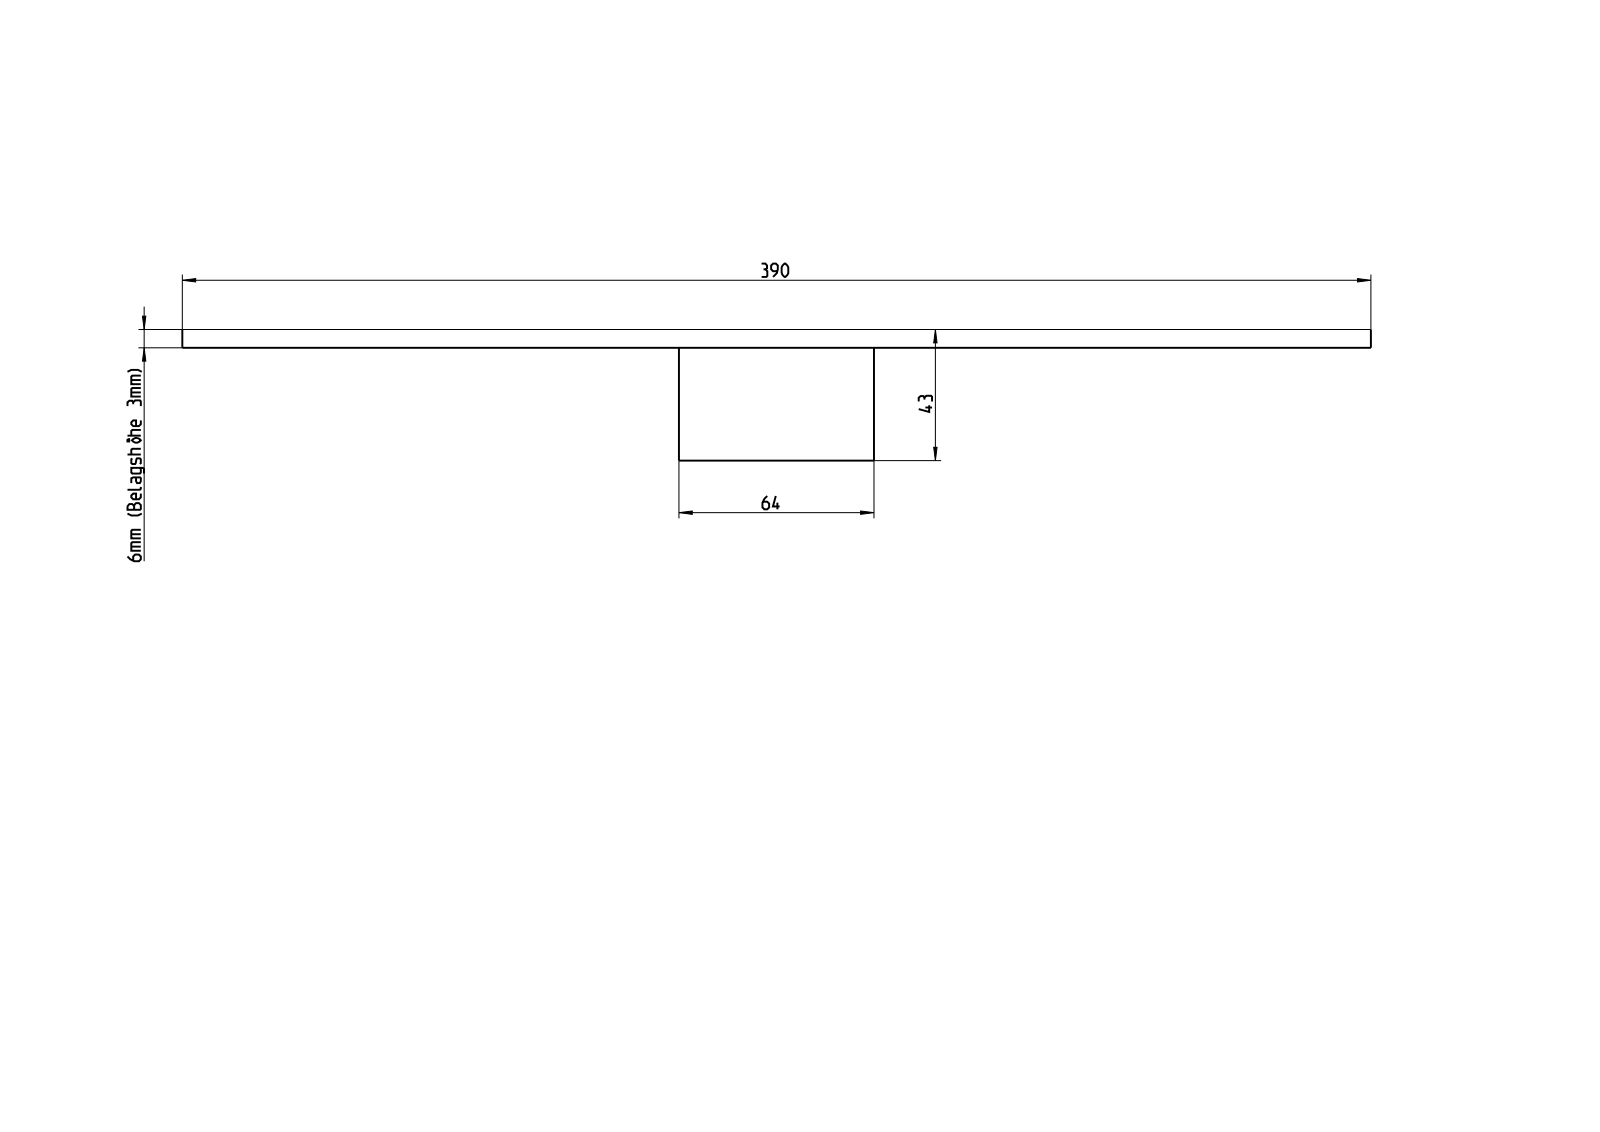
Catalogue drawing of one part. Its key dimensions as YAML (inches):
part_name: "1BKG4002W3LA; AUSLASS; BKG4002W3LA_ASM"
step_written_by: "CREO PARAMETRIC BY PTC INC, 2022024 (AUTOMOTIVE_DESIGN)"
units: inches
bodies: {solids: 2, faces: 16, planar: 16, cylindrical: 0, other: 0}
overall_size: [19.646, 15.354, 1.693]
volume: 76.58
surface_area: 633.9
face_to_face_distances: [0.236, 1.457, 15.354, 1.693, 19.646, 18.189, 6.415, 8.935, 2.52, 8.939]
